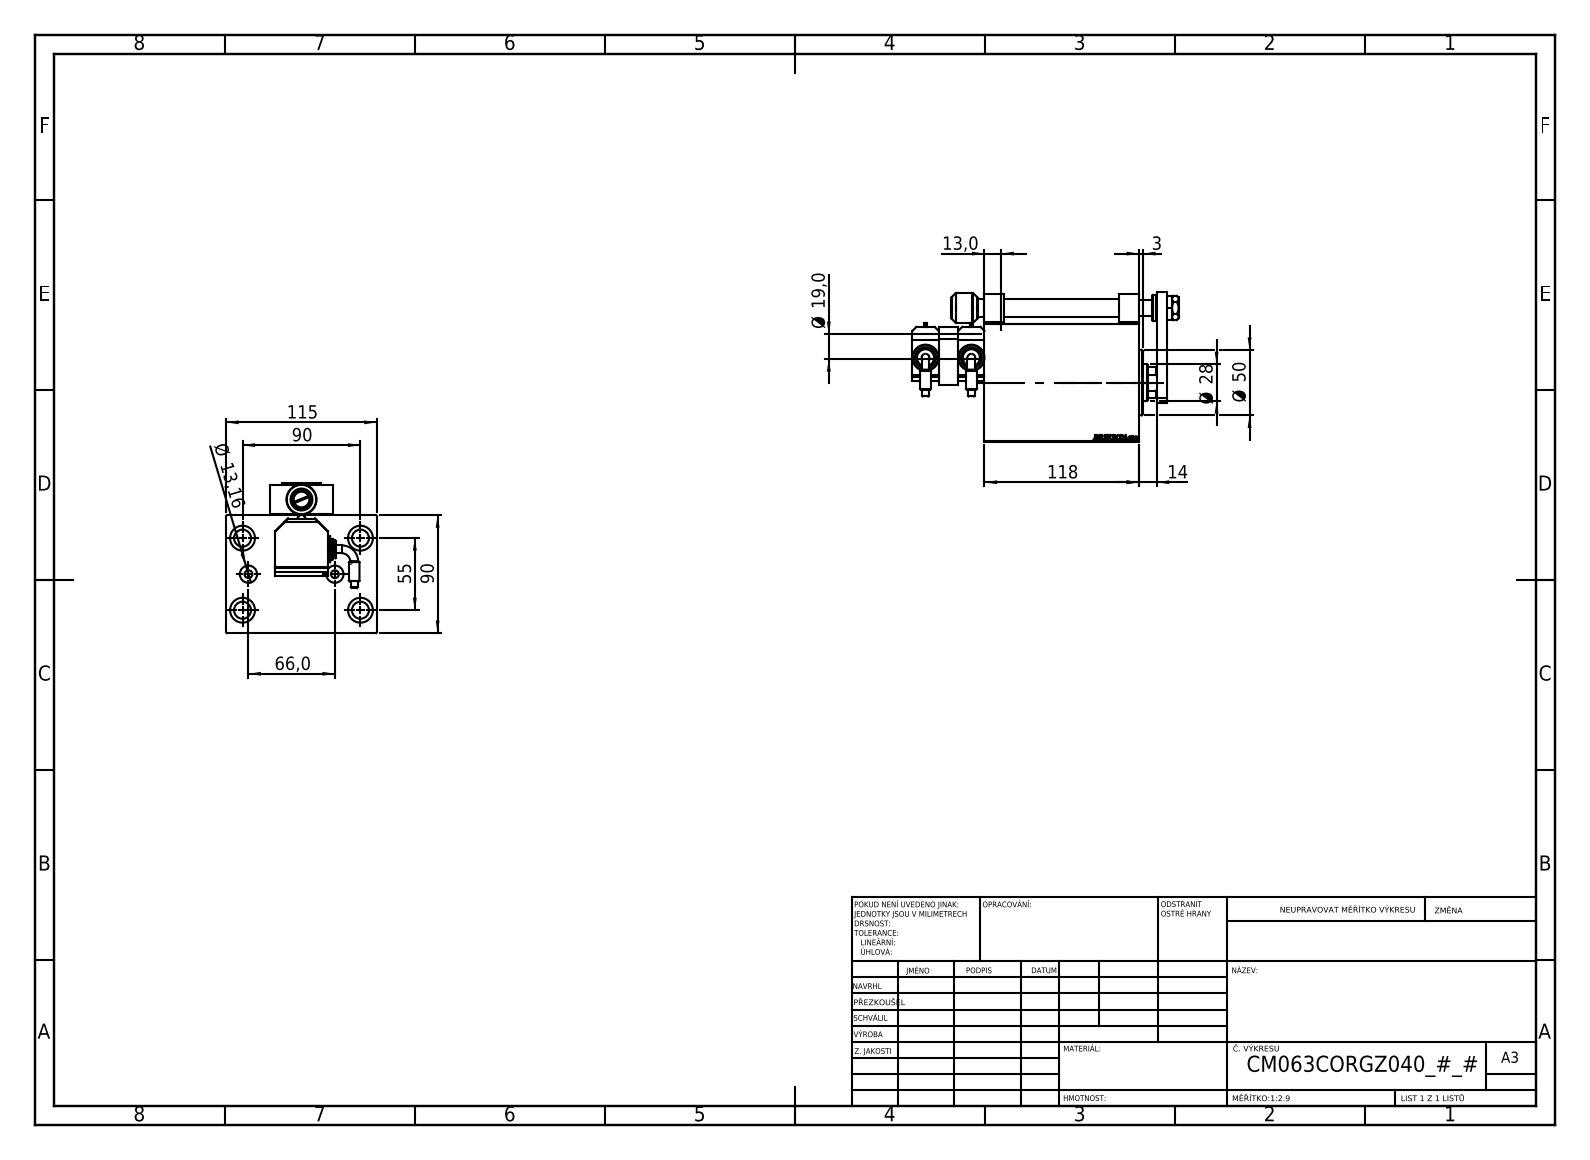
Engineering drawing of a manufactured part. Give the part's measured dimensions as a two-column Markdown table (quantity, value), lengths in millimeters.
| quantity | value |
| --- | --- |
| part name | V450CM_C_Body; V450CM_C_VCP; SWITCH_P_FRONT_BACK; NUT_D16 (+7 more) |
| STEP written by | SolidWorks 2019 (CONFIG_CONTROL_DESIGN) |
| units | millimeters |
| bodies | 13 solids, 1113 faces (524 planar, 124 cylindrical, 465 other) |
| overall size | 203.2 × 115 × 114.5 |
| volume | 389 820 mm³ |
| surface area | 196 337 mm² |
| round holes (diameter × count) | 13 × 5, 4 × 4, 8 × 4, 19 × 4, 6 × 2, 13.16 × 2, 12 × 1, 14 × 1, 16.5 × 1, 18.5 × 1, 28 × 1, 31.5 × 1 |
| round bosses / shafts (diameter × count) | 20 × 3, 16 × 2, 14 × 2, 8 × 2, 6 × 2, 5.04 × 2, 50 × 1, 23 × 1 |
| partial cylindrical surfaces (radius × count) | 3 × 1, 13.5 × 1 |
| main face-to-face distances | 90, 115, 35, 118, 17.5, 100.5, 37.5, 13.5, 139.5, 15 |
| hole center spacings | 52.74, 20, 27.87, 33.71, 53.81, 55, 75.67, 89.81 |
